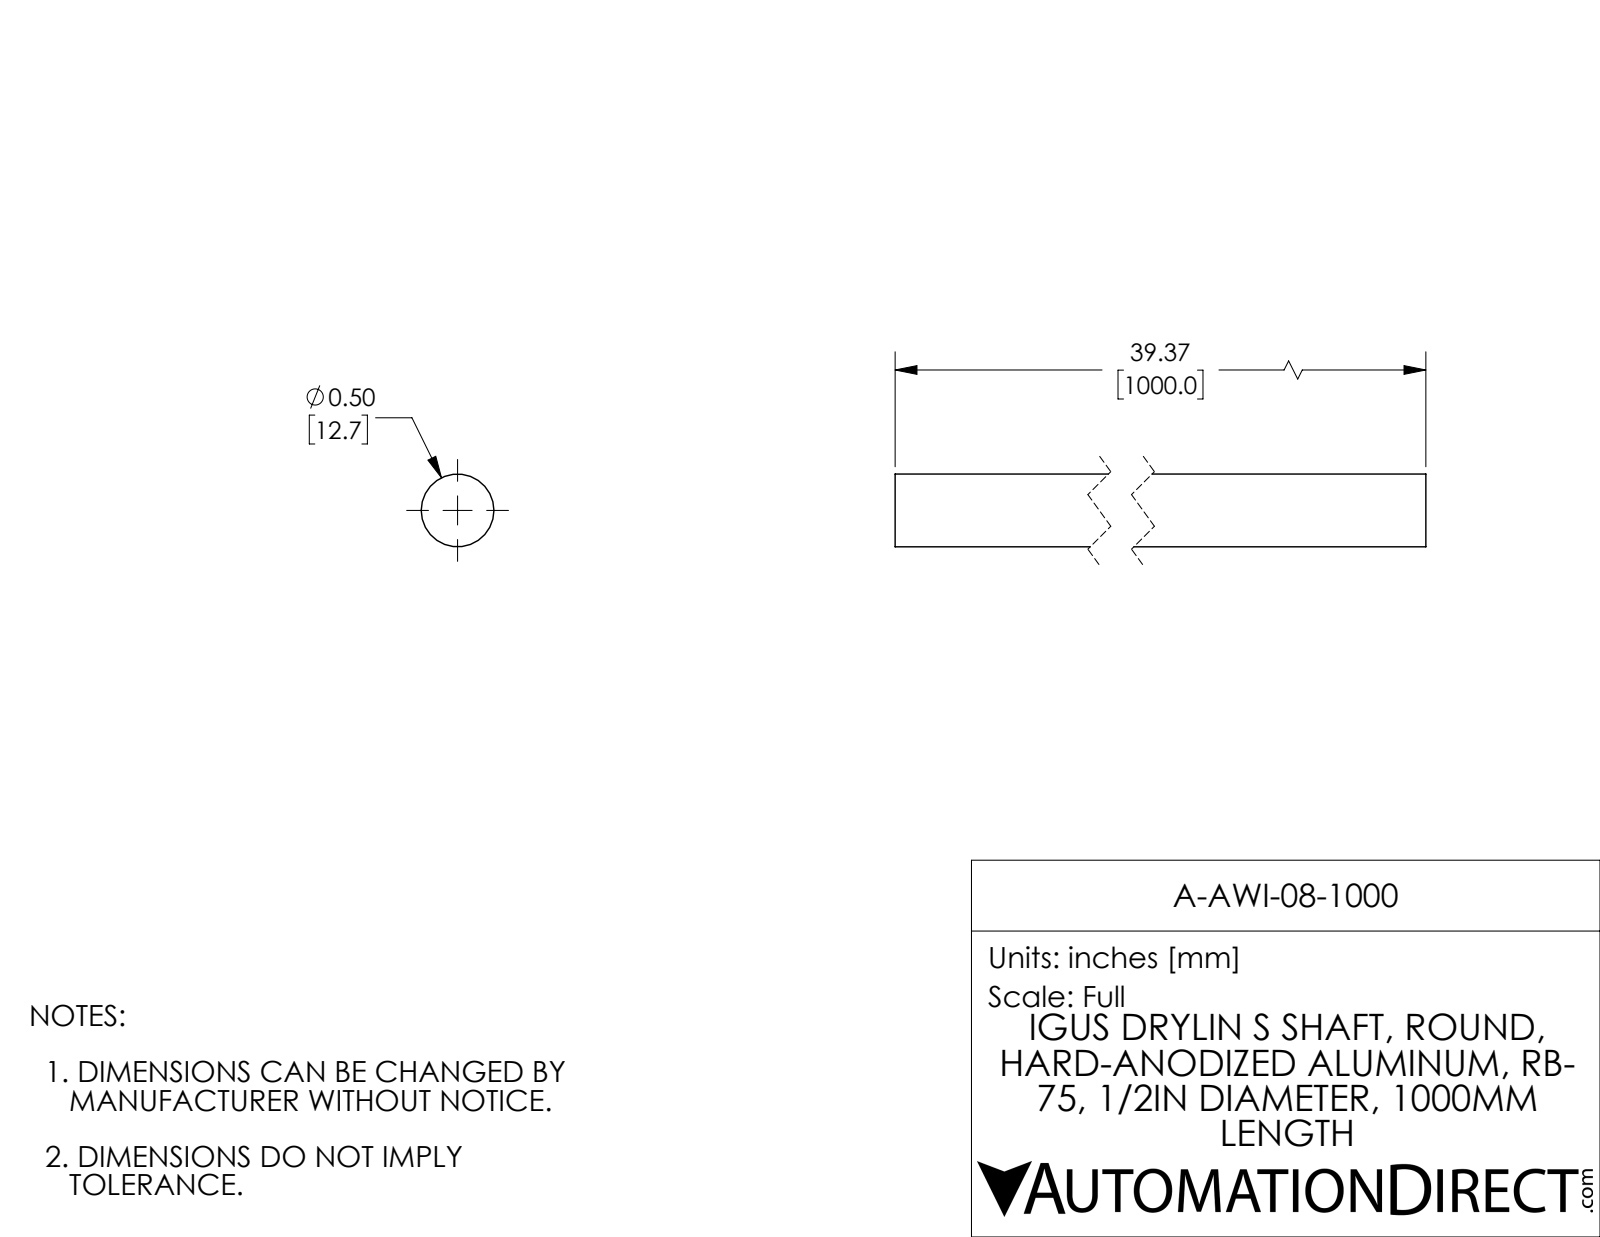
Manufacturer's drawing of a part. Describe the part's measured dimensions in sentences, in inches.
The part is named "A-AWI-08-1000". Its 3-D file was written by "SolidWorks 2017 (AUTOMOTIVE_DESIGN)". It is 1 solid with 4 faces: 2 planar, 2 cylindrical and 0 other. Overall it measures 39.37 by 0.5 by 0.5 inches. Its volume is 7.73 cubic inches and its surface area 62.24 square inches. Round bosses or shafts: 1 of diameter 0.5. The main face-to-face distances are 39.37.
